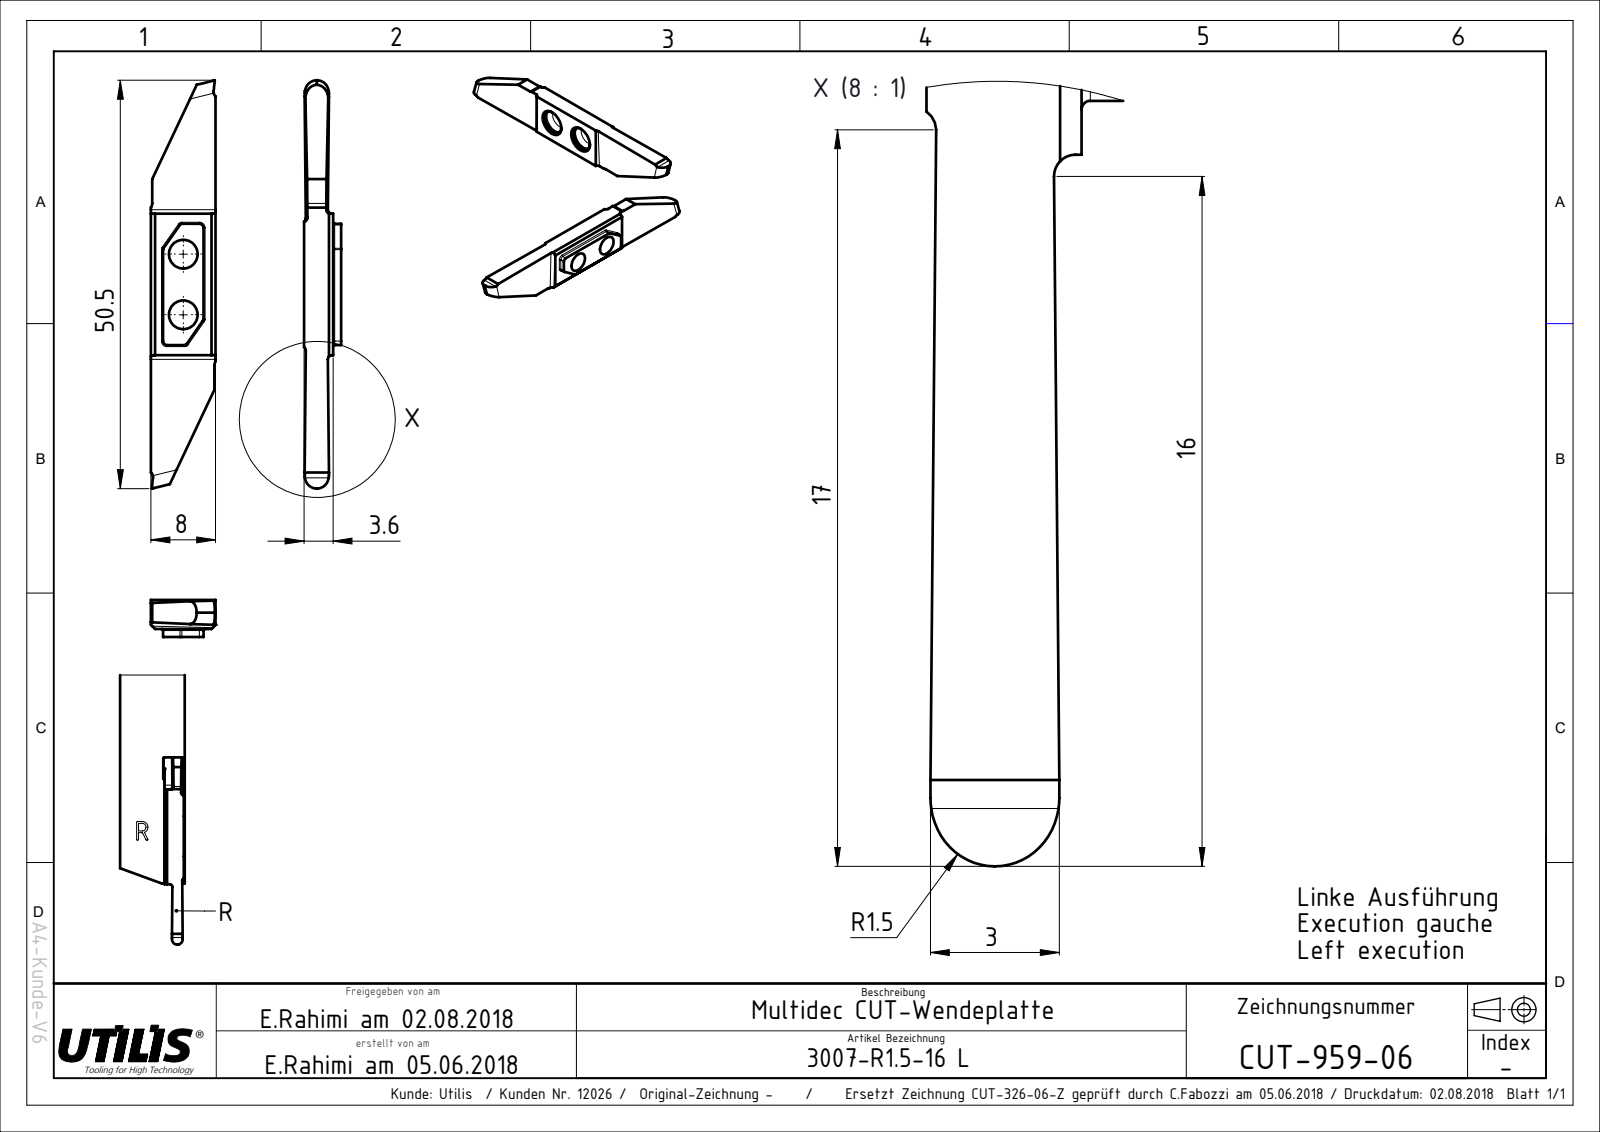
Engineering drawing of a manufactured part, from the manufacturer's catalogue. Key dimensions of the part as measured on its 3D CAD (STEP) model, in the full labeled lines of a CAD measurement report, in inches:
Part name (STEP PRODUCT): CUT-959; ASME Y14.5
STEP written by: FormatWorks Professional (AP242_MANAGED_MODEL_BASED_3D_ENGINEERING_MIM_LF)
Units: inches
Bodies: 1 solid, 40 faces (22 planar, 18 cylindrical, 0 other)
Overall size (bounding box): 1.988 × 0.315 × 0.142
Volume: 0.056 in³ · Surface area: 1.567 in²
Round holes (diameter × count): ⌀0.14 ×2
Partial cylindrical surfaces — rounded edges, fillets, slot ends (radius × count): R0.02 ×4, R0.059 ×4, R0.031 ×2, R0.039 ×2
Main face-to-face distances: 0.093, 0.142, 0.315, 0.712, 0.309, 0.303, 0.276, 0.039, 0.65, 0.689
Hole centre spacings: 0.295
